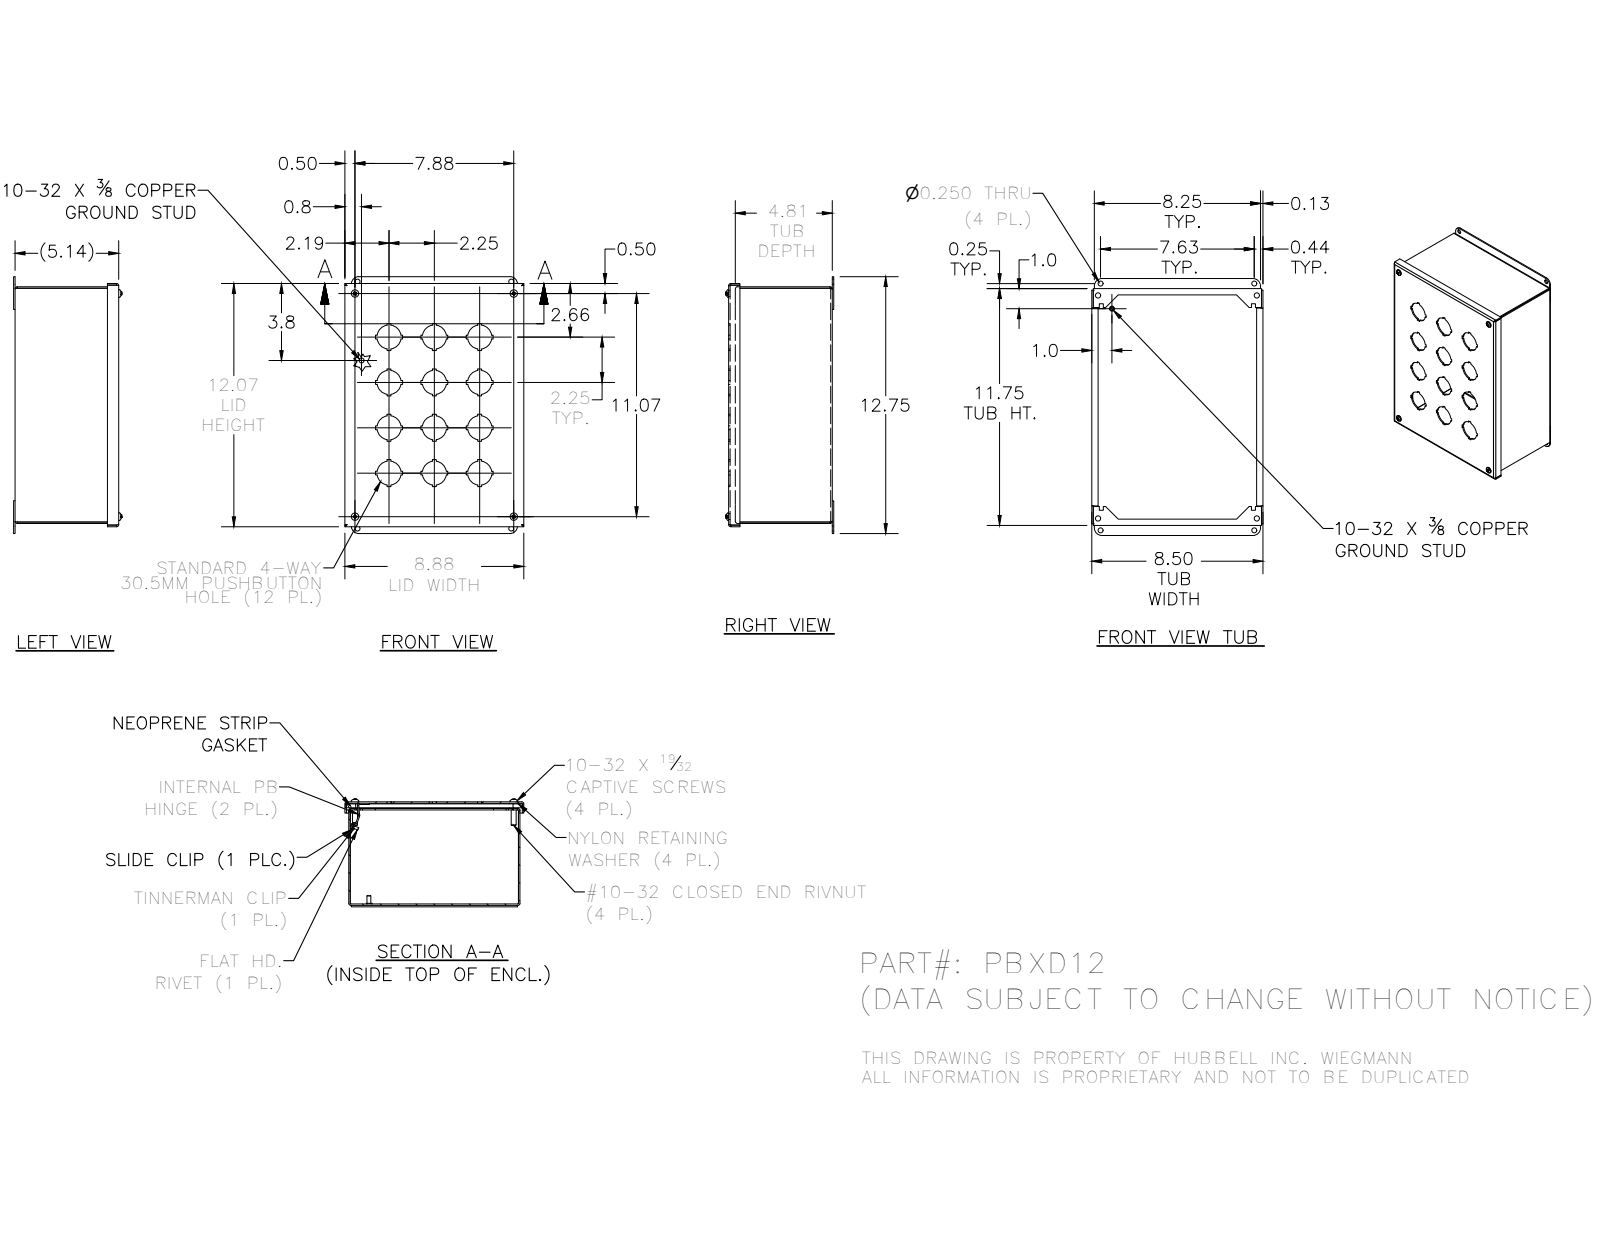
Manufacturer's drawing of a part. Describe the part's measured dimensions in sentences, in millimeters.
The part is named "PBXD12LID; 372163; 39077; PBXD12BKP (+8 more)". Its 3-D file was written by "Autodesk Inventor 2016 (AUTOMOTIVE_DESIGN)". It is 25 solids with 801 faces: 507 planar, 180 cylindrical and 114 other. Overall it measures 323.85 by 225.55 by 135.79 millimeters. Its volume is 608 241 cubic millimeters and its surface area 625 951 square millimeters. Round holes: 12 of diameter 30.48, 4 of diameter 3.96, 4 of diameter 4.98, 4 of diameter 6.35, 4 of diameter 6.53, 4 of diameter 7.06, 4 of diameter 7.14, 4 of diameter 7.95, 2 of diameter 3.56. Round bosses or shafts: 6 of diameter 4.83, 4 of diameter 11.51, 4 of diameter 10.31, 4 of diameter 9.47, 4 of diameter 6.3, 3 of diameter 6.35, 1 of diameter 3.17. Partial cylindrical surfaces (rounded edges, fillets, slot ends): 12 of radius 0.79, 12 of radius 2.67, 6 of radius 4.78, 4 of radius 2.27, 4 of radius 2.29, 4 of radius 9.53, 3 of radius 0.8, 3 of radius 1.59. The main face-to-face distances are 1.88, 128.73, 130.61, 214.02, 126.85, 296.57, 215.9, 212.14, 298.45, 294.69. The hole center spacings are 57.15, 127.79, 80.82, 114.3, 80.34, 133.06, 161.64, 174.52.
